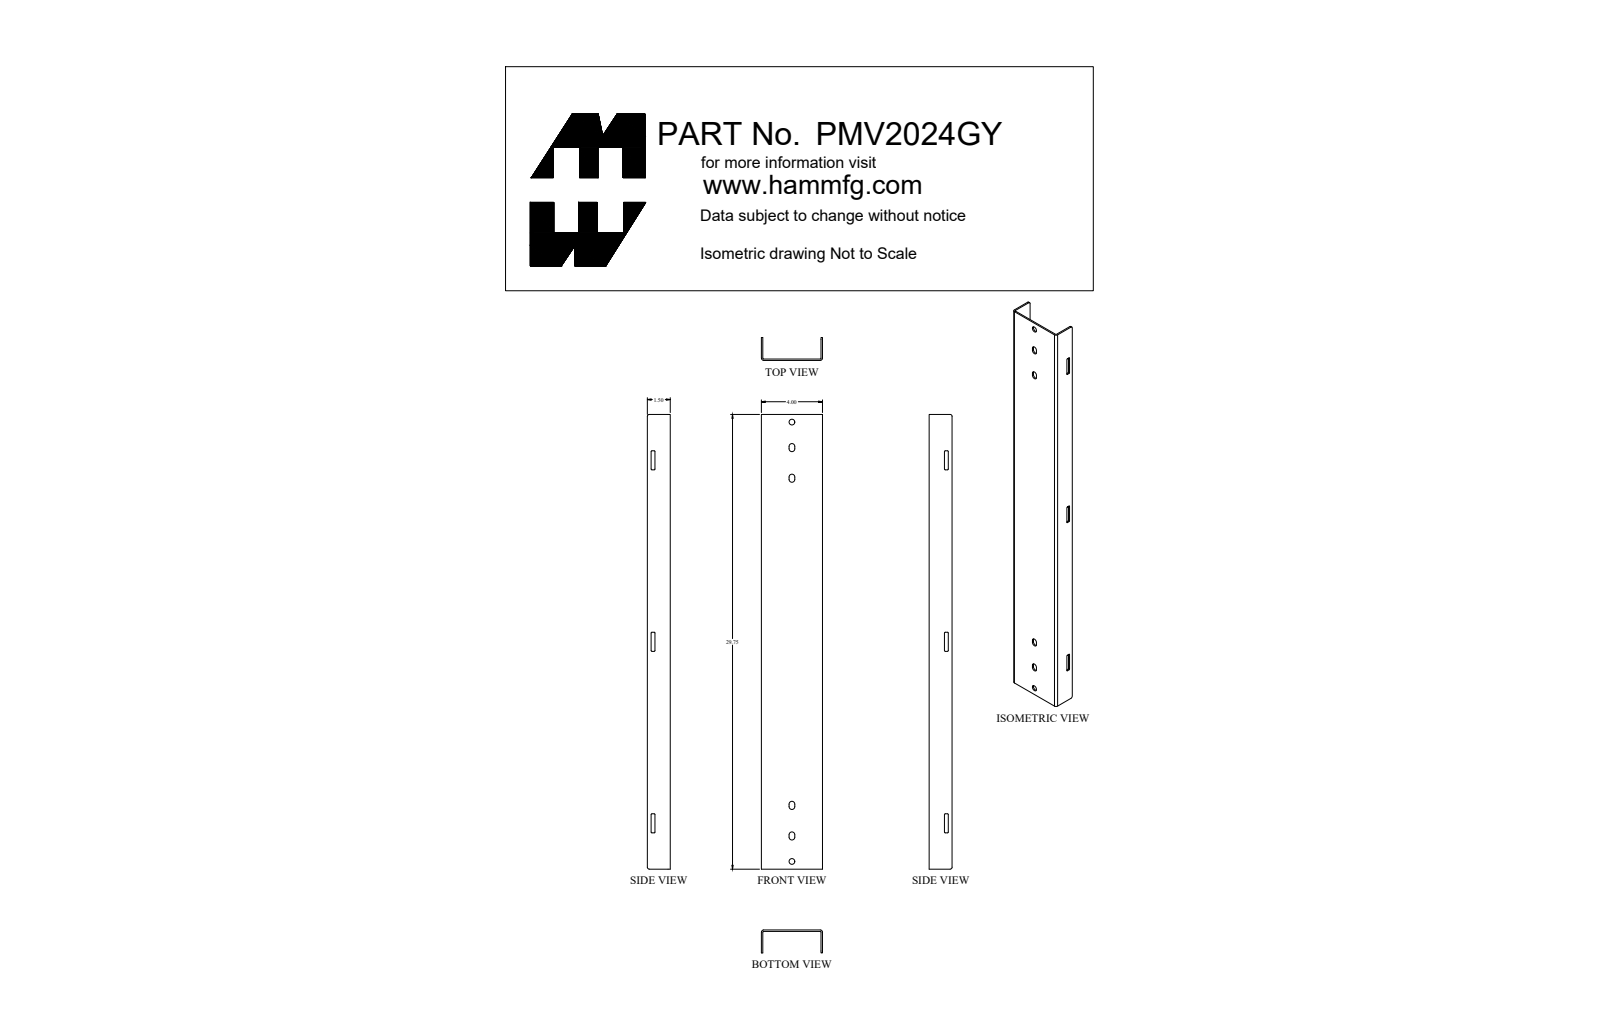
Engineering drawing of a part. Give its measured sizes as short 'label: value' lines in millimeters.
name: PMV2024GY
written by: SolidWorks 2018 (AUTOMOTIVE_DESIGN)
unit: mm
bodies: 1 solid, 90 faces (42 planar, 48 cylindrical, 0 other)
size: 755.7 × 101.6 × 38.1
volume: 307 300 mm³; area: 260 700 mm²
holes: 2× ⌀9.5
rounds: 12× R1.3, 8× R4.8, 2× R1.2, 2× R3.2, 2× R3.6
face distances: 2.4, 99.2, 101.6, 96.8, 38.1, 35.7, 6.4, 31.8, 25.4, 23
hole spacings: 730.3
